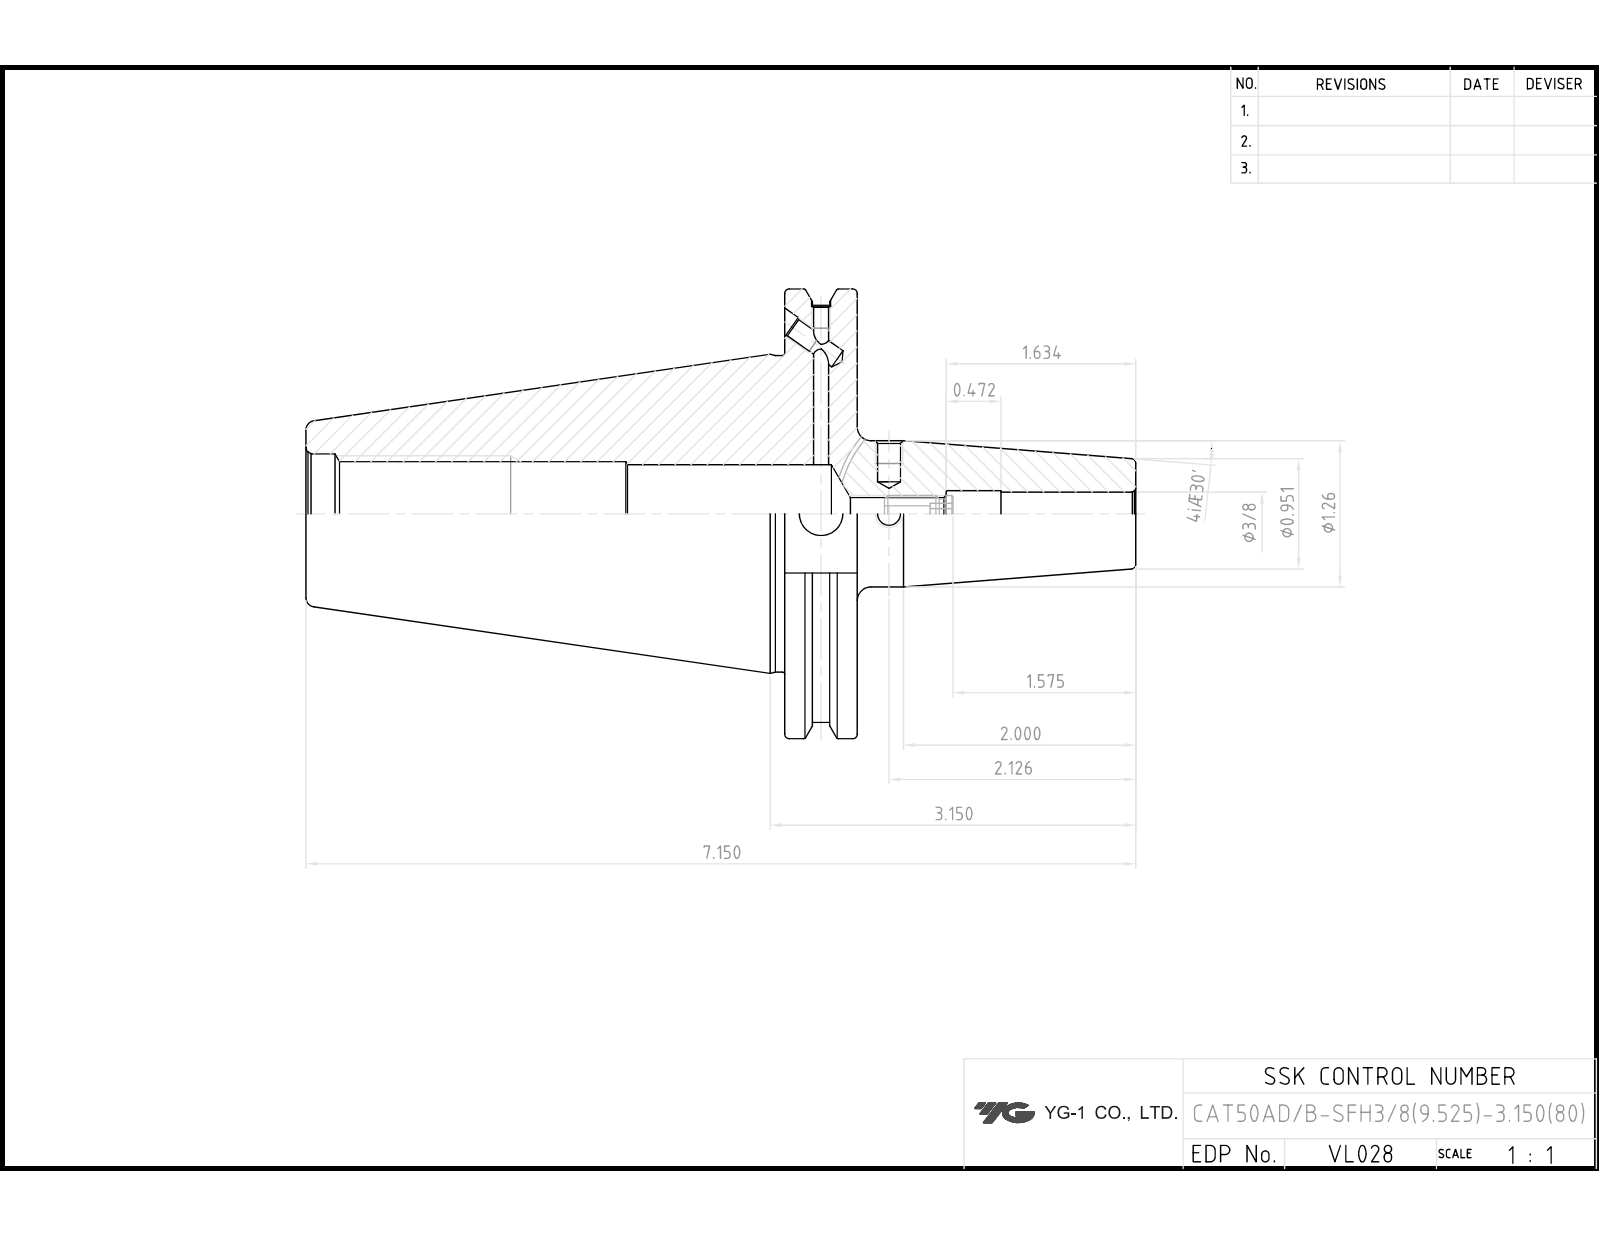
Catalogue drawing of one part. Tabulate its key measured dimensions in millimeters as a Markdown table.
| quantity | value |
| --- | --- |
| part name | LO-CAT50ADB-SFH9.525-80 |
| STEP written by | Autodesk Inventor 2025 (AUTOMOTIVE_DESIGN) |
| units | millimeters |
| bodies | 1 solid, 84 faces (37 planar, 26 cylindrical, 21 other) |
| overall size | 181.6 × 98.42 × 94.69 |
| volume | 358 293 mm³ |
| surface area | 51 483 mm² |
| round holes (diameter × count) | 3.24 × 2, 4.13 × 2, 4.2 × 2, 5 × 2, 9.53 × 2, 6.92 × 1, 10.72 × 1, 21.97 × 1, 26.2 × 1 |
| round bosses / shafts (diameter × count) | 98.42 × 1, 91.29 × 1, 69.25 × 1, 32 × 1 |
| main face-to-face distances | 15.88, 104.77, 120.65, 73.03, 25.9, 181.6, 76.83, 60.95, 110.82, 6.05 |
